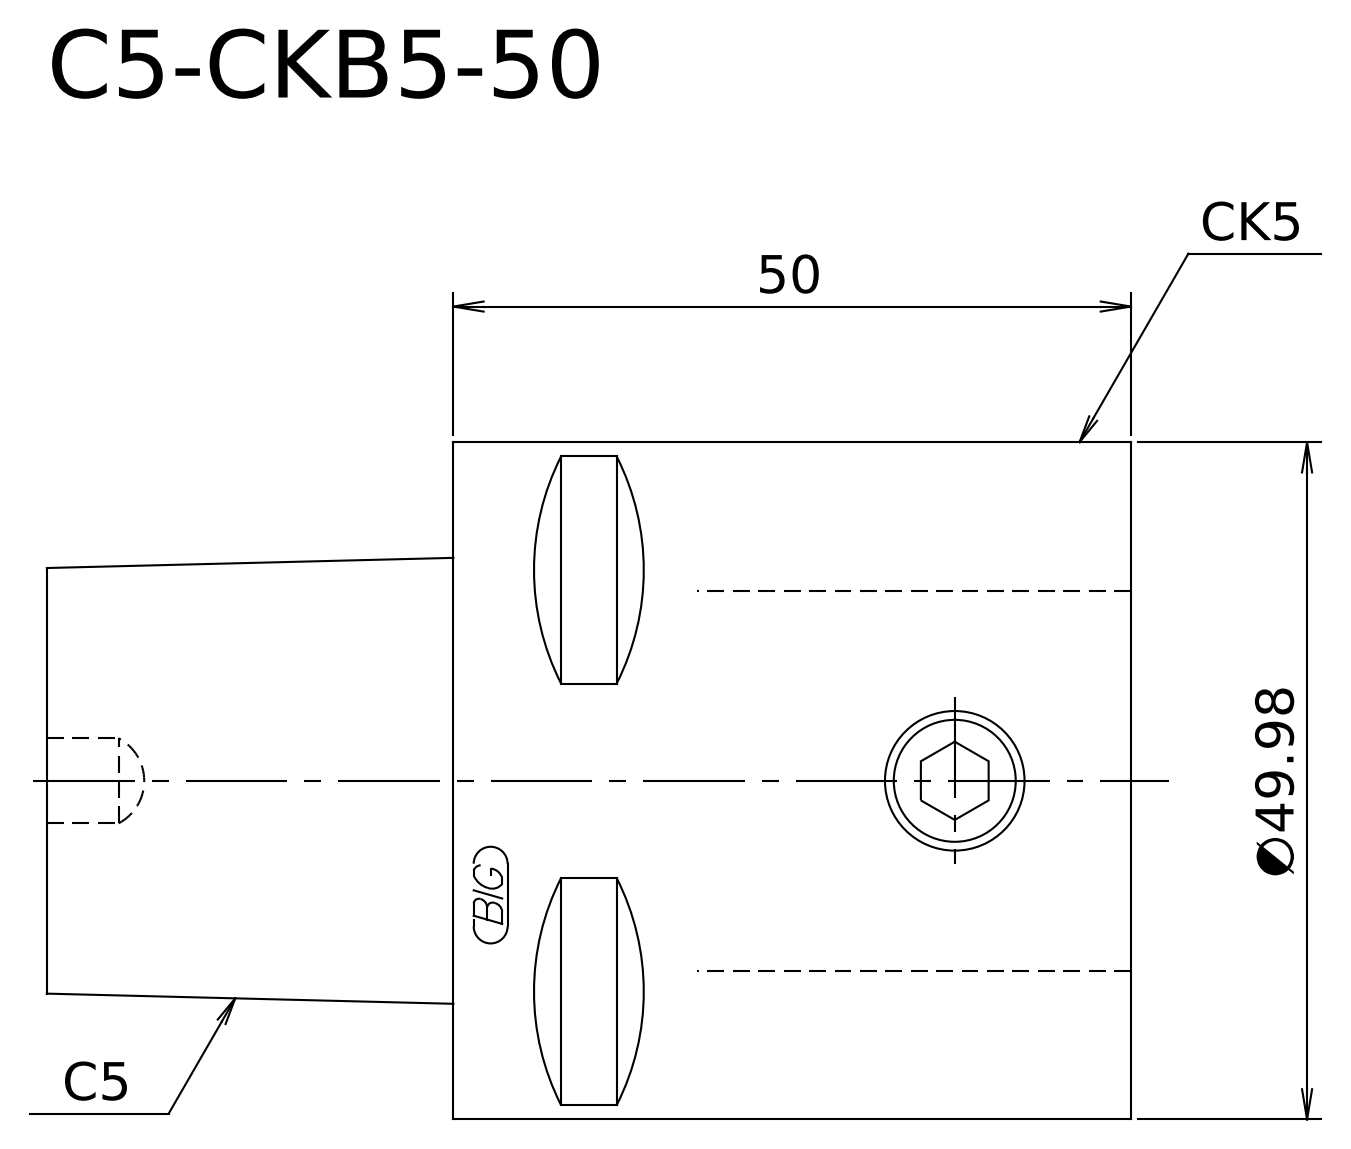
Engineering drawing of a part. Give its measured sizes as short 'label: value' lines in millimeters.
written by: Kubotek KeyCreator V8.5.1 (14335) (CONFIG_CONTROL_DESIGN)
unit: mm
bodies: 1 solid, 5 faces (3 planar, 1 cylindrical, 1 other)
size: 80 × 49.98 × 49.98
volume: 125 342 mm³; area: 14 936 mm²
bosses: 1× ⌀49.98
face distances: 50, 80, 30
